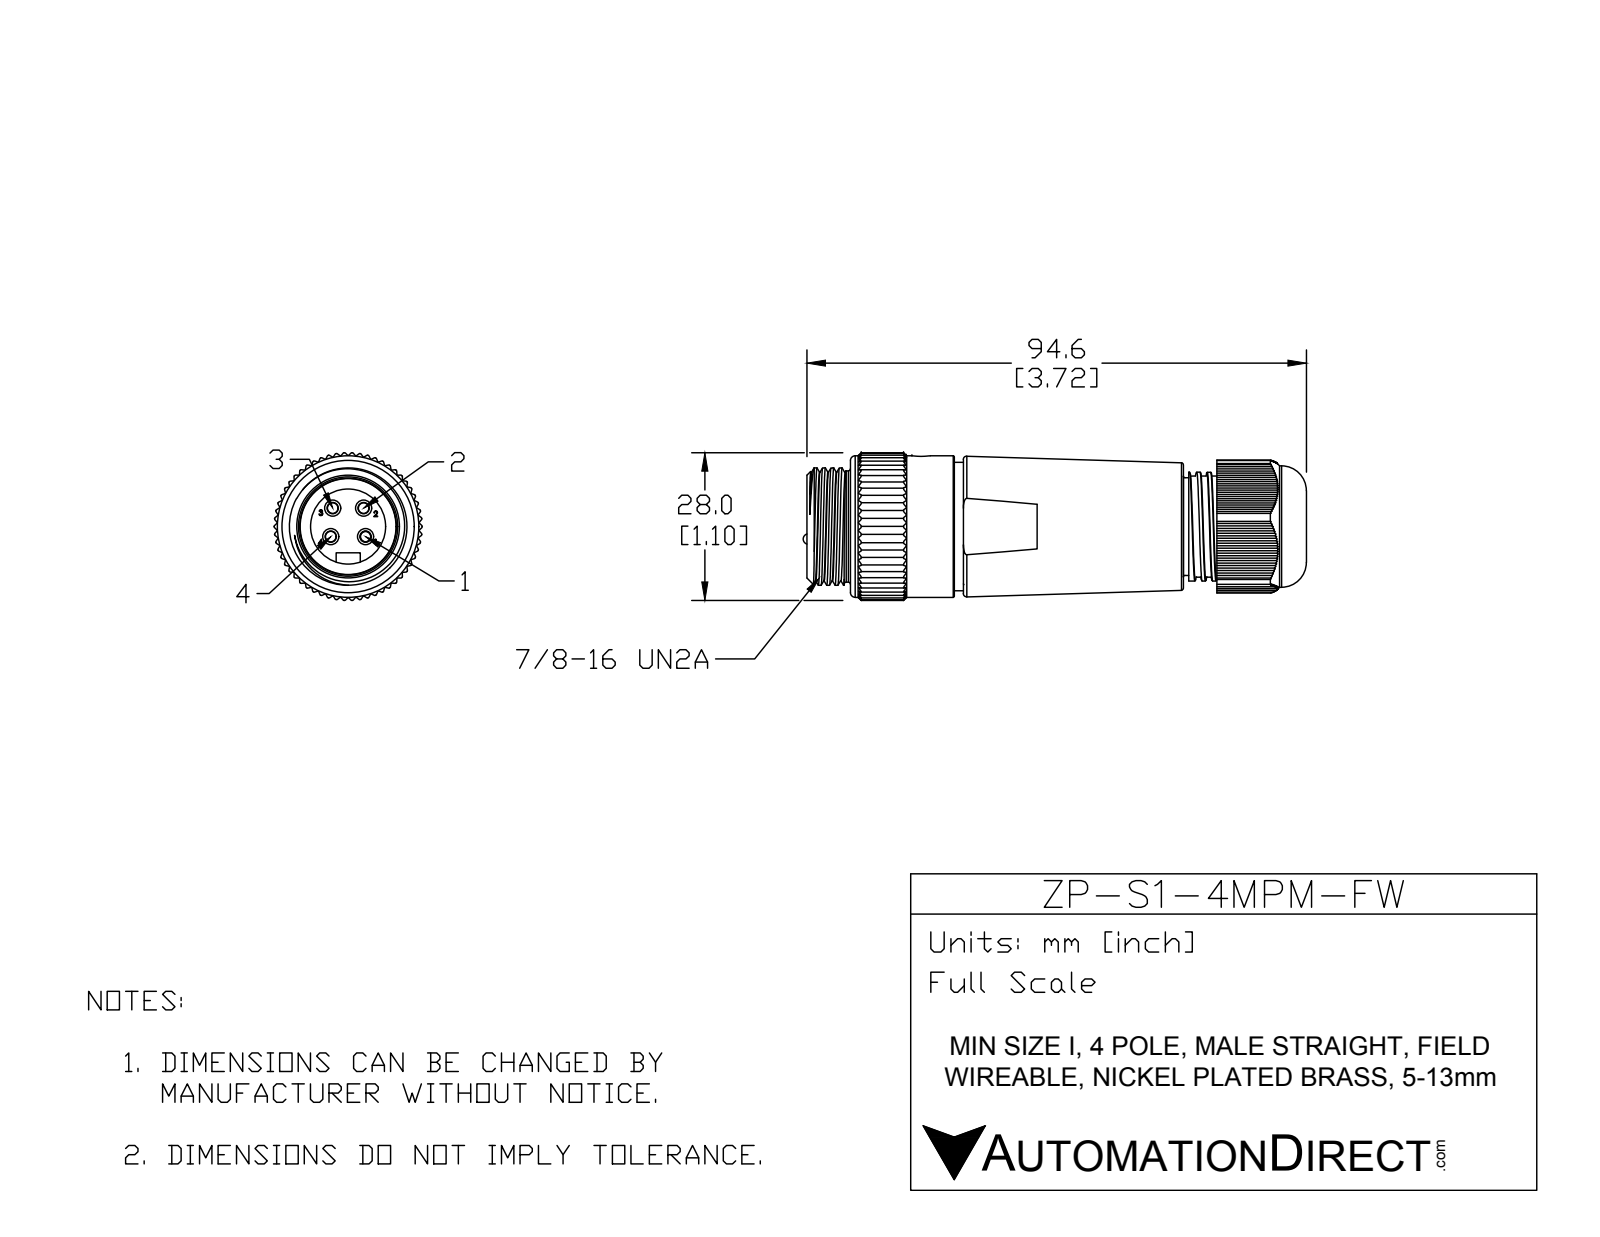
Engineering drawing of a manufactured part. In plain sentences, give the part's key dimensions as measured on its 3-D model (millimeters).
The part is named "MIN-4MPM-FW". Its 3-D file was written by "SolidWorks 2015 (AUTOMOTIVE_DESIGN)". It is 1 solid with 873 faces: 465 planar, 332 cylindrical and 76 other. Overall it measures 94.56 by 28 by 27.96 millimeters. Its volume is 43 488 cubic millimeters and its surface area 12 692 square millimeters. Round holes: 1 of diameter 3.5, 1 of diameter 13.46, 1 of diameter 14.22, 1 of diameter 18.29, 1 of diameter 25.4. Round bosses or shafts: 4 of diameter 3.05, 4 of diameter 2, 1 of diameter 26.8, 1 of diameter 24.3, 1 of diameter 24, 1 of diameter 22.99, 1 of diameter 22.23, 1 of diameter 21.06. Partial cylindrical surfaces (rounded edges, fillets, slot ends): 116 of radius 0.25, 58 of radius 0.2, 1 of radius 2.29, 1 of radius 13.23, 1 of radius 14. The main face-to-face distances are 0.36, 0.72, 1.08, 1.44, 16.56, 1.8, 16.92, 16.2, 69.78, 6.35.
